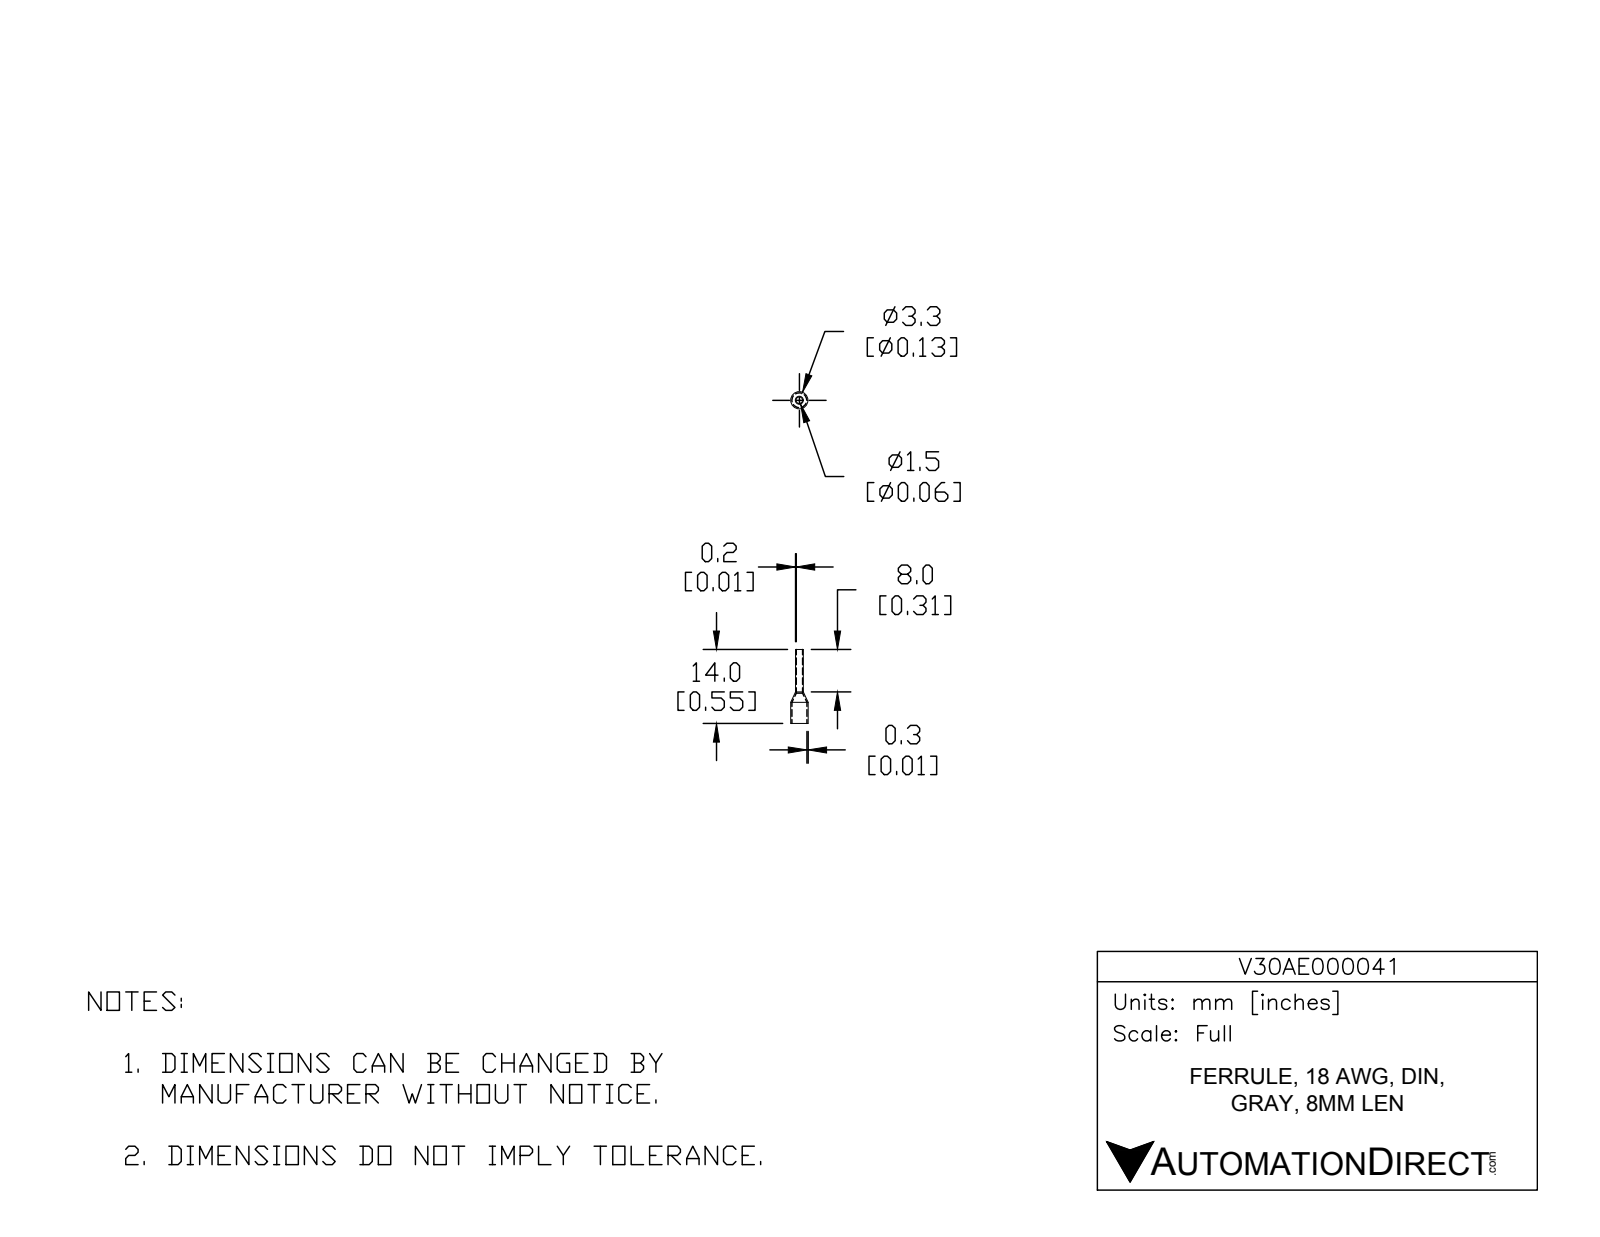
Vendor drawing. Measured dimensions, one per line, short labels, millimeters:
name: V30AE000041
written by: SolidWorks 2017 (AUTOMOTIVE_DESIGN)
unit: mm
bodies: 1 solid, 14 faces (2 planar, 8 cylindrical, 4 other)
size: 14 × 3.3 × 3.3
volume: 18 mm³; area: 177 mm²
holes: 1× ⌀1.2, 1× ⌀2.8
bosses: 1× ⌀3.3, 1× ⌀1.5
face distances: 14
